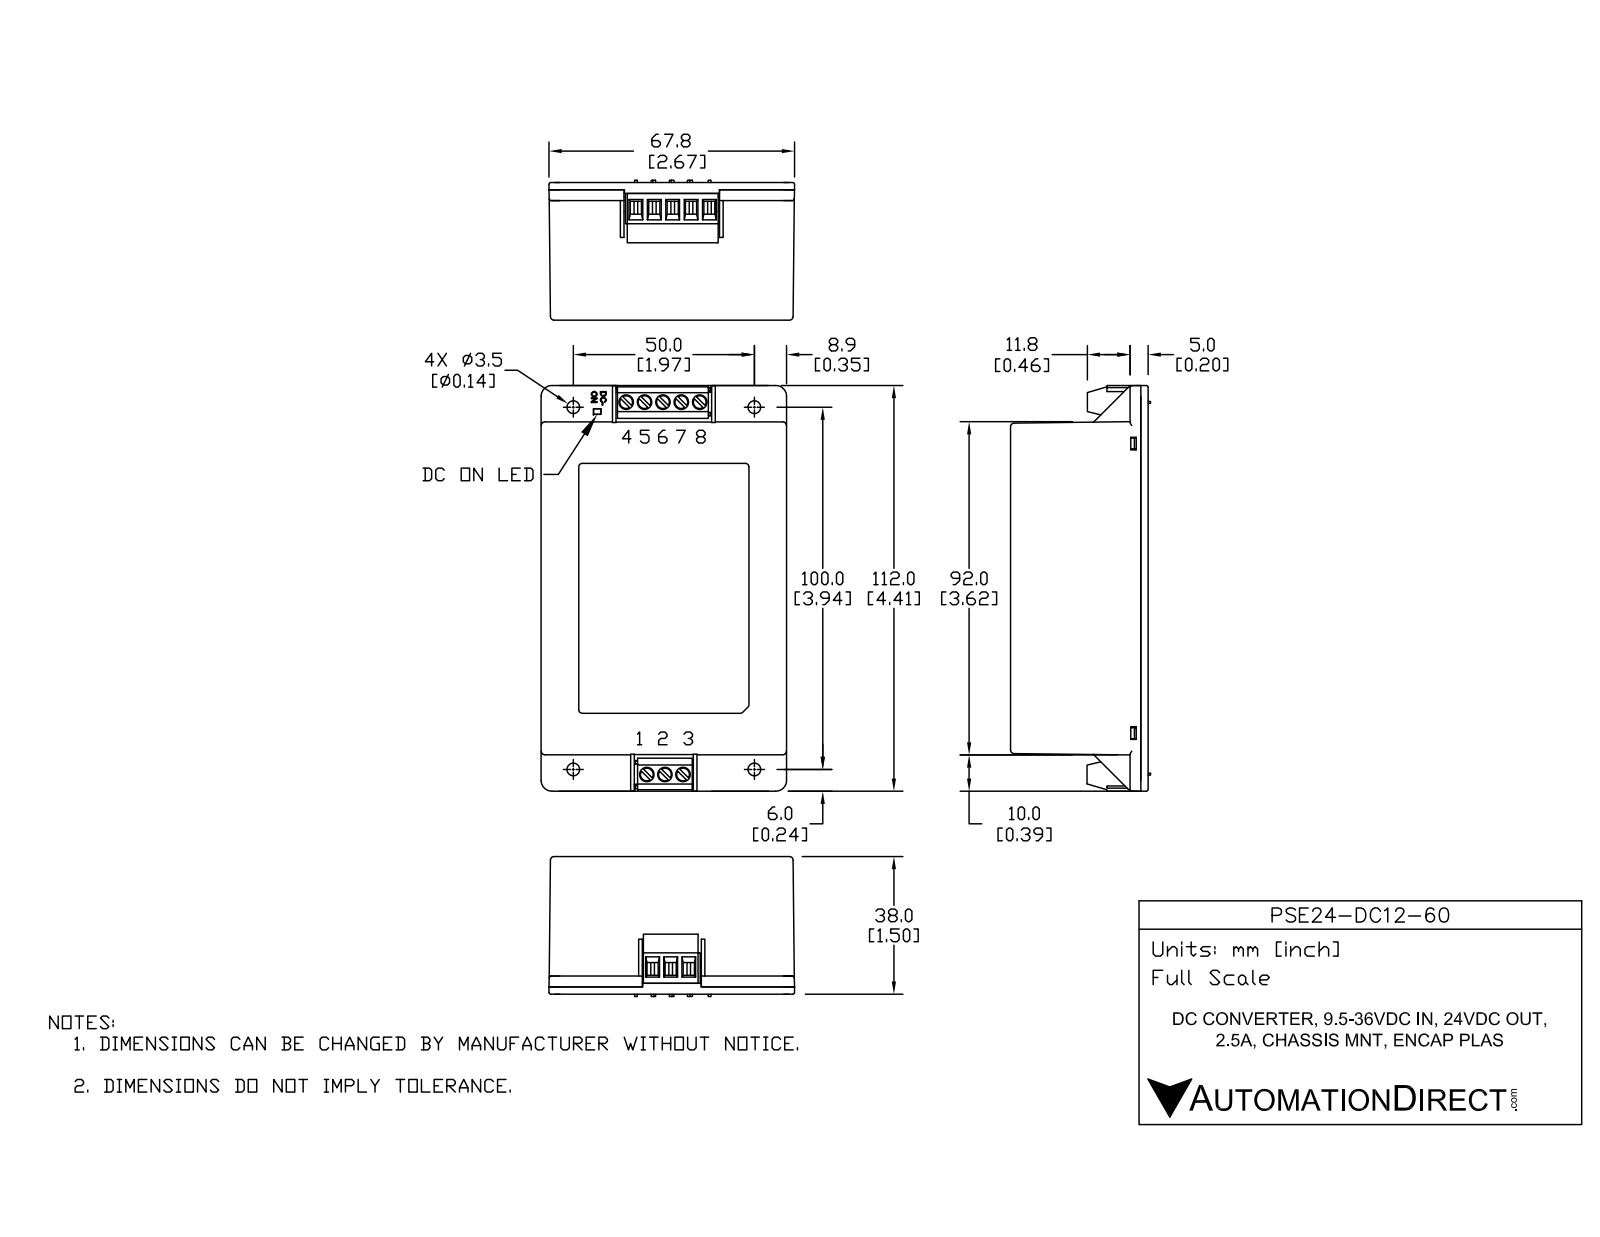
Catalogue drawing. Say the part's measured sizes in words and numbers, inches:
The part is named "PSE24-DC12-60". Its 3-D file was written by "SolidWorks 2015 (AUTOMOTIVE_DESIGN)". It is 0 solids with 390 faces: 282 planar, 89 cylindrical and 19 other. Overall it measures 4.446 by 2.728 by 1.459 inches. Round holes: 10 of diameter 0.157, 4 of diameter 0.138, 1 of diameter 0.097, 1 of diameter 0.161, 1 of diameter 0.256. Round bosses or shafts: 4 of diameter 0.059, 1 of diameter 0.197. Partial cylindrical surfaces (rounded edges, fillets, slot ends): 17 of radius 0.039, 8 of radius 0.02, 4 of radius 0.085, 4 of radius 0.104, 4 of radius 0.118, 3 of radius 0.128. The main face-to-face distances are 0.039, 0.039, 1.378, 1.339, 0.028, 0.04, 0.067, 1.311, 1.378, 1.338. The hole center spacings are 0.2, 0.4, 1.969, 4.021, 4.027, 0.197, 0.6, 3.937.
